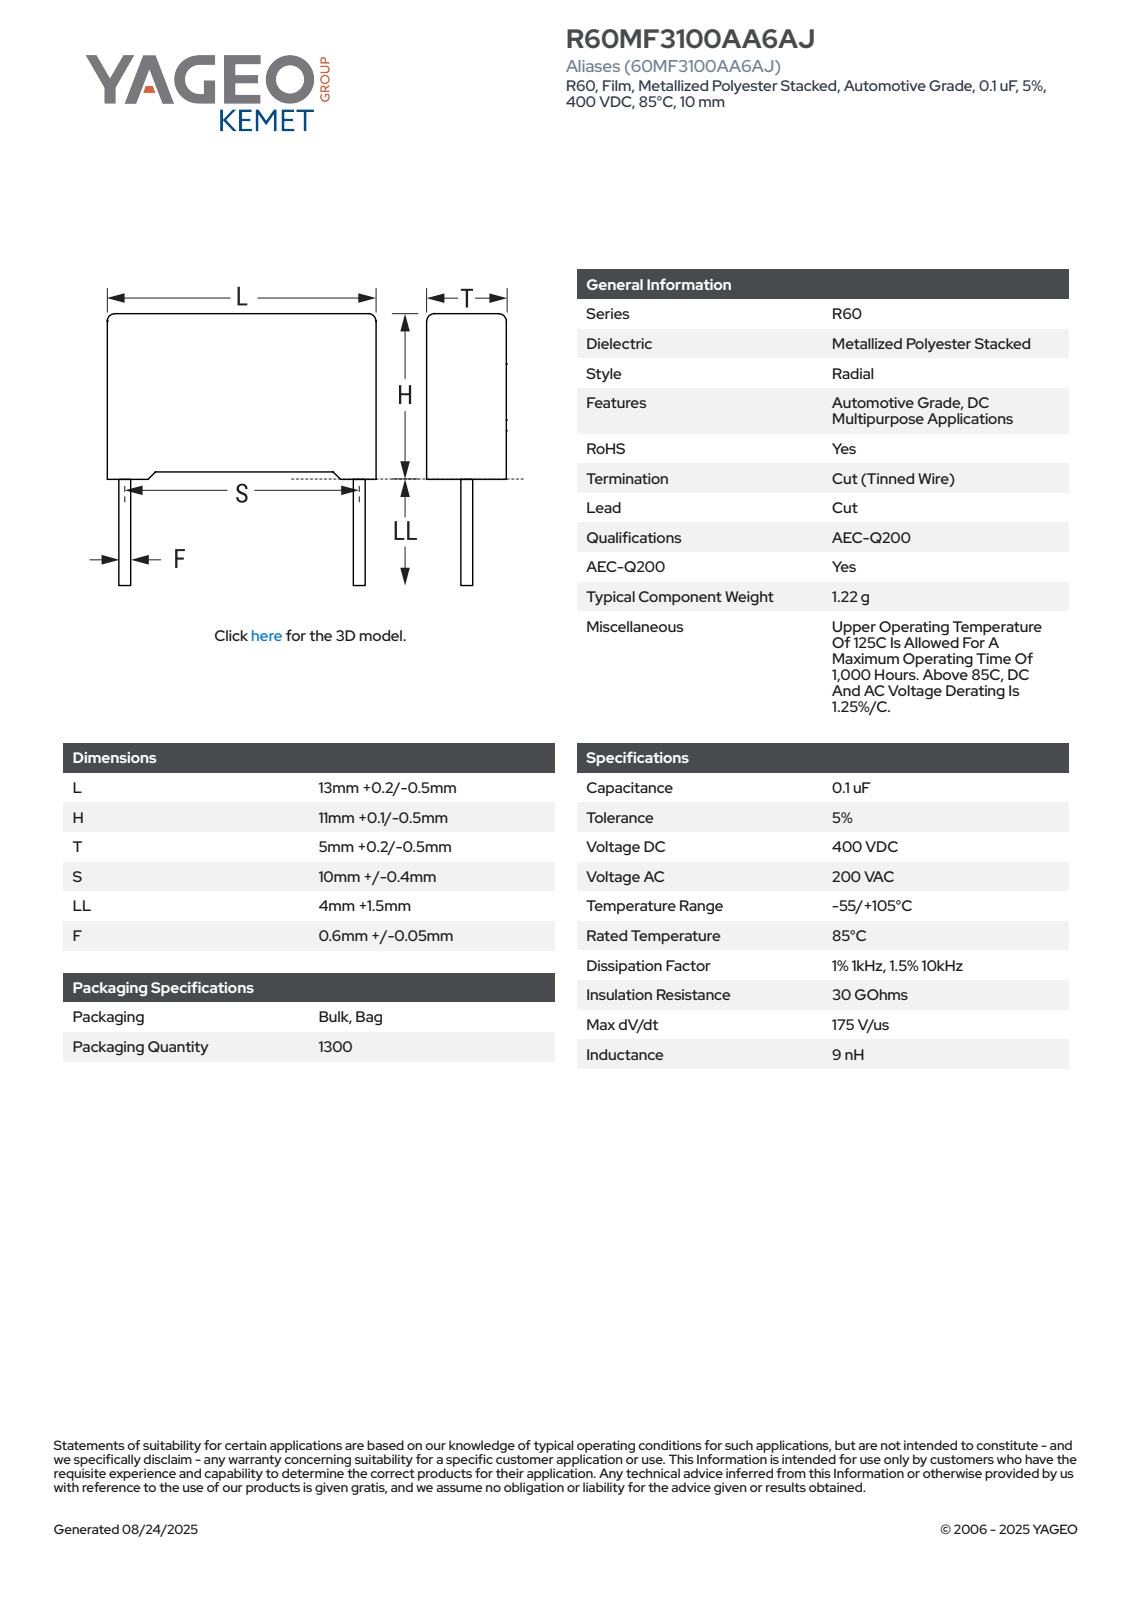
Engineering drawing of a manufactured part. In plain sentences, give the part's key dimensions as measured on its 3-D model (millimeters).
The part is named "CFR_RB2_13X11X5_L13.2H11.1T5.2S10LL5.5F0.65". Its 3-D file was written by "SolidWorks 2021 (AUTOMOTIVE_DESIGN)". It is 4 solids with 85 faces: 77 planar, 8 cylindrical and 0 other. Overall it measures 16.6 by 13.2 by 5.21 millimeters. Its volume is 722 cubic millimeters and its surface area 592 square millimeters. Round bosses or shafts: 2 of diameter 0.65. Partial cylindrical surfaces (rounded edges, fillets, slot ends): 4 of radius 0.5. The main face-to-face distances are 5.2, 13.2, 10.35, 0.44, 4.76, 0.75, 11.1, 4.32, 12.76, 0.37.
